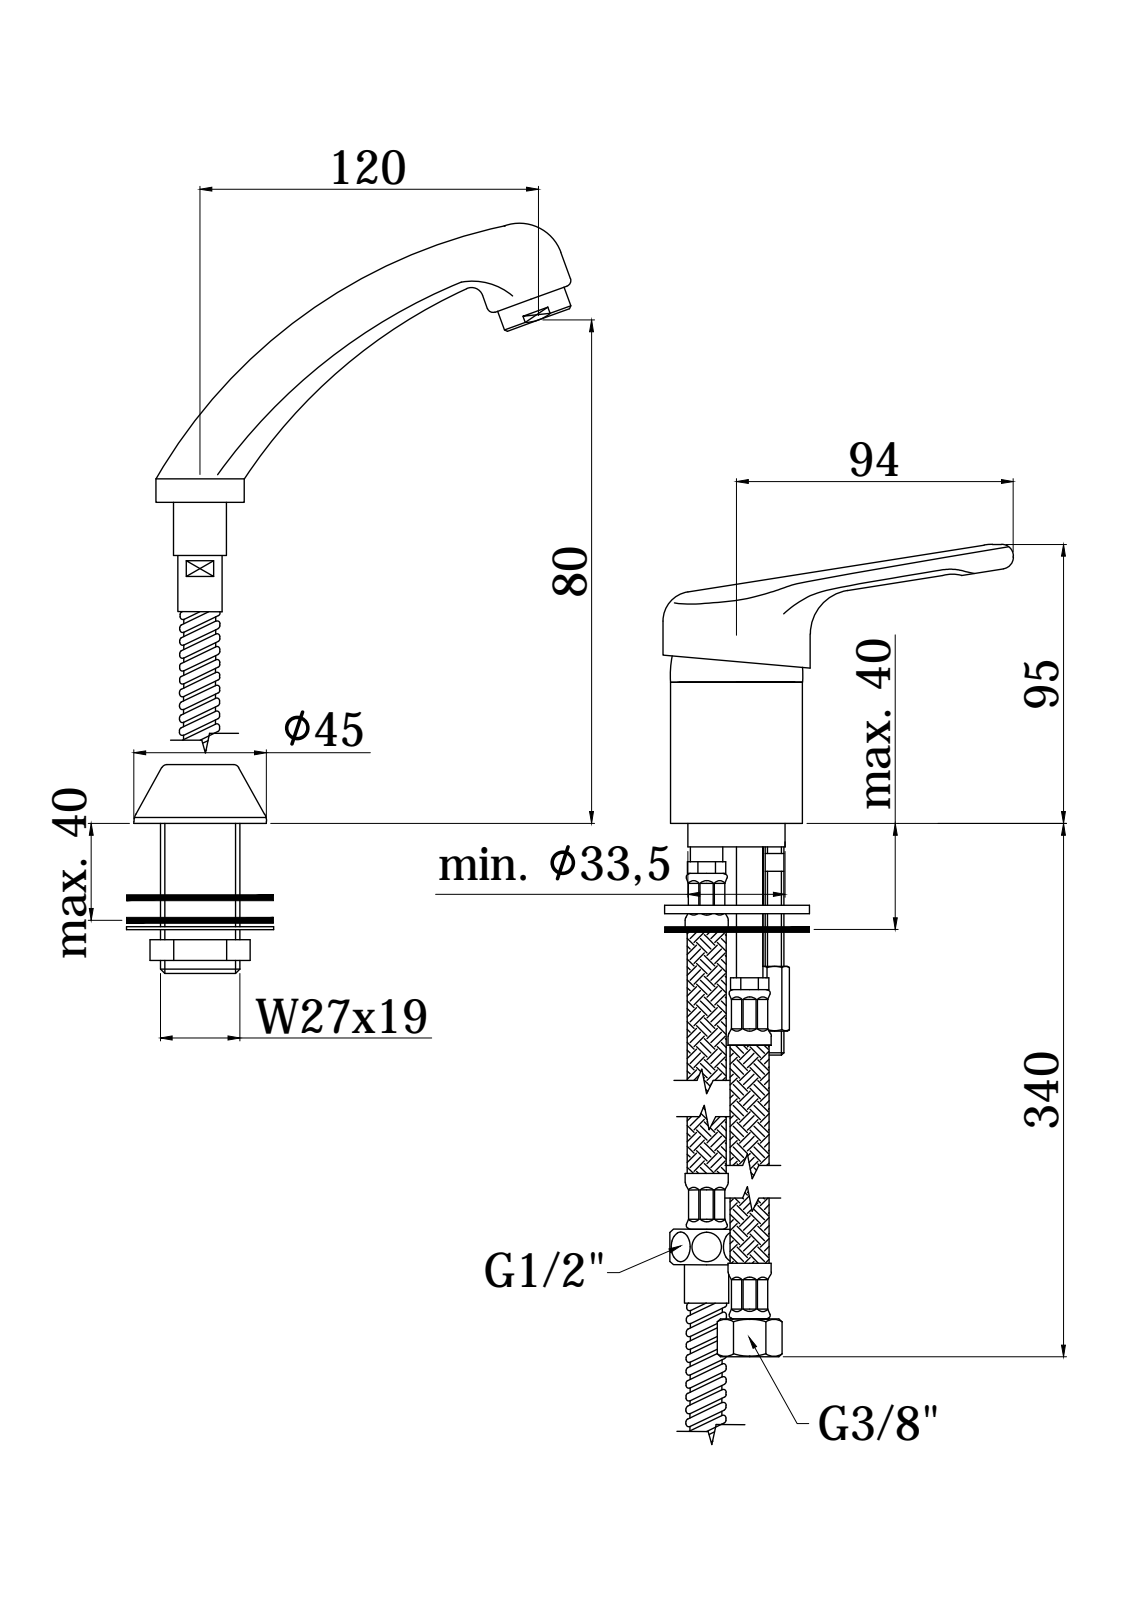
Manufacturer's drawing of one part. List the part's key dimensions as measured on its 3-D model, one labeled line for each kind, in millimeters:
Part name (STEP PRODUCT): NT087CR
STEP written by: CREO PARAMETRIC BY PTC INC, 2020044 (CONFIG_CONTROL_DESIGN)
Units: millimetres
Bodies: 5 solids, 2443 faces (1944 planar, 275 cylindrical, 224 other)
Overall size (bounding box): 164.87 × 148 × 110.45
Volume: 179 466 mm³ · Surface area: 75 280 mm²
Round holes (diameter × count): ⌀8 ×5, ⌀9 ×3, ⌀11.7 ×2, ⌀3 ×1, ⌀3.3 ×1, ⌀4 ×1, ⌀4.5 ×1, ⌀5 ×1, ⌀6 ×1, ⌀9.4 ×1, ⌀11 ×1, ⌀11.6 ×1
Round bosses / shafts (diameter × count): ⌀50 ×1, ⌀48 ×1, ⌀46 ×1, ⌀41 ×1, ⌀39.5 ×1, ⌀36.7 ×1, ⌀33 ×1, ⌀31 ×1
Partial cylindrical surfaces — rounded edges, fillets, slot ends (radius × count): R0.2 ×24, R0.5 ×16, R1 ×5, R2 ×4, R135 ×2, R3.9 ×1, R4.75 ×1, R7 ×1
Main face-to-face distances: 1.5, 6.5, 36.8, 8, 12.6, 43.3, 5, 2.5, 18.3, 7.96
Hole centre spacings: 13.46, 14.43, 3.5, 9.9, 14, 0.54, 1.51, 2
